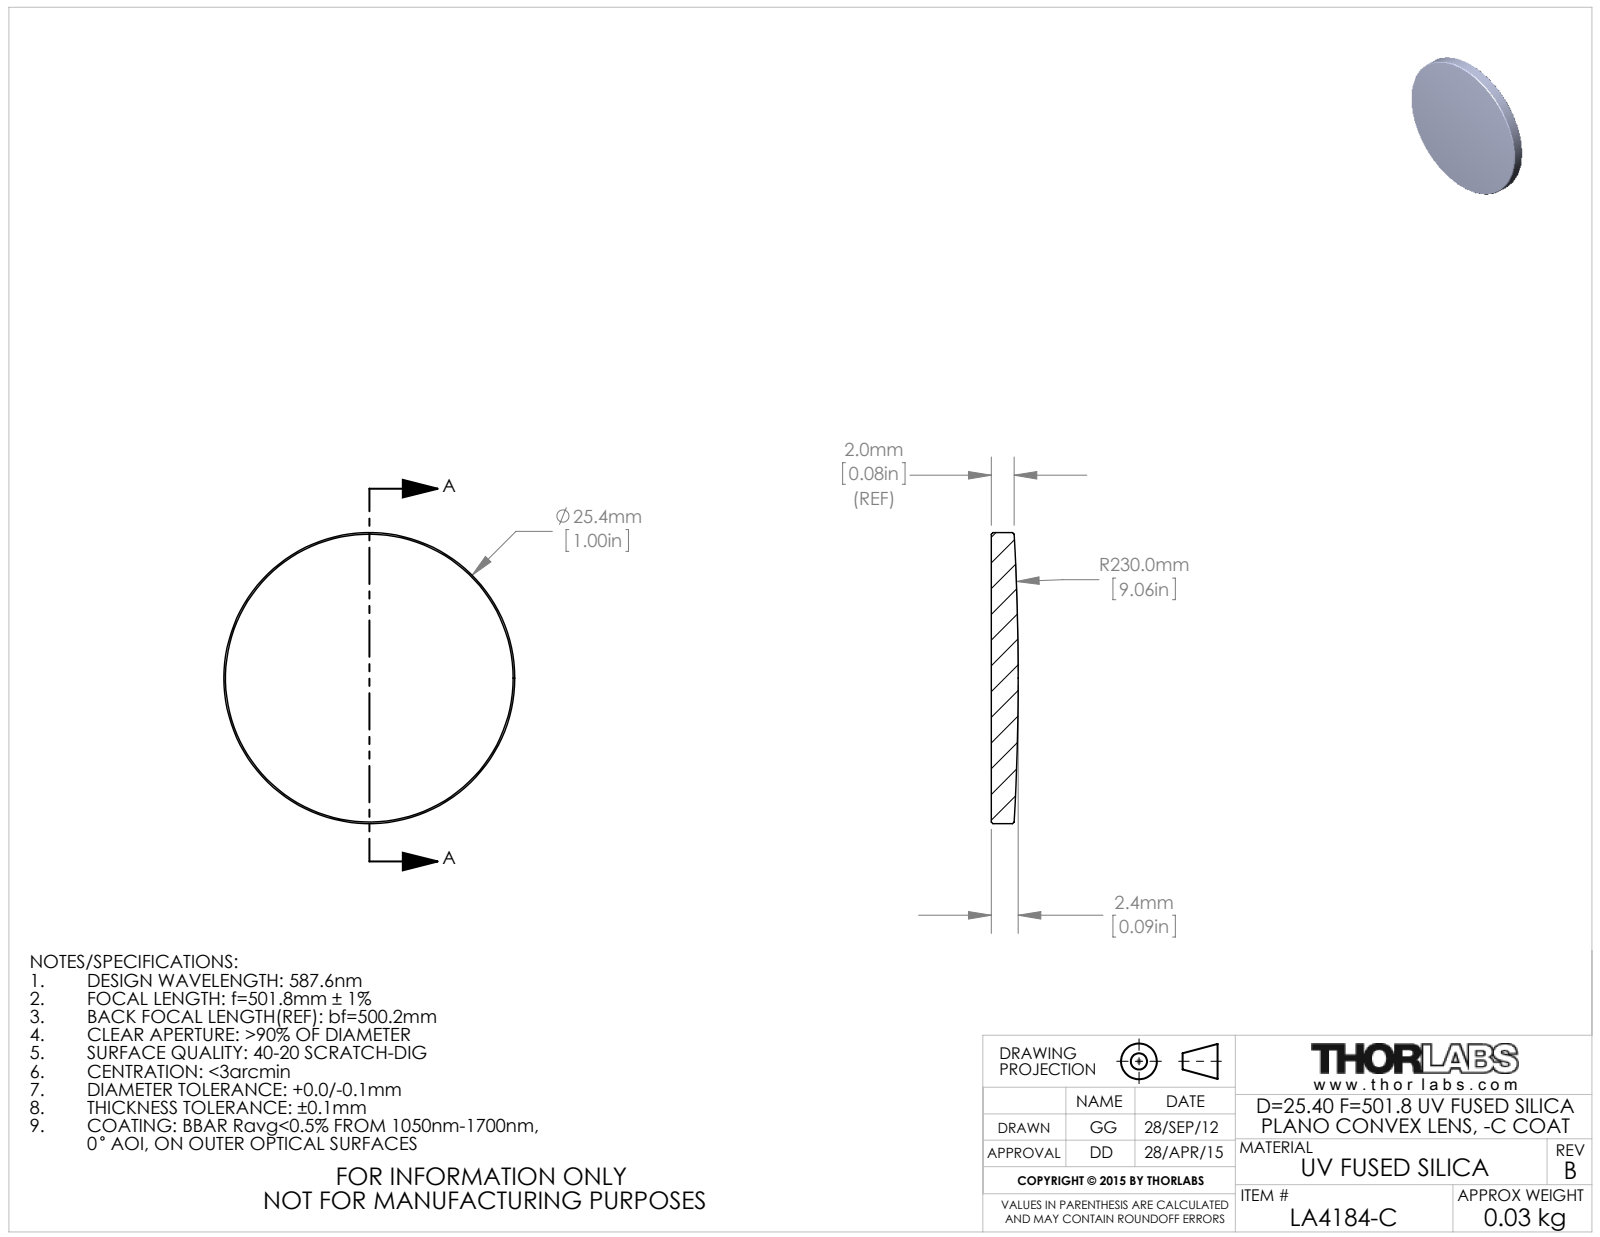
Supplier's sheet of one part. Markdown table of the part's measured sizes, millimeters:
| quantity | value |
| --- | --- |
| part name | 25004-E0W |
| STEP written by | SolidWorks 2014 (CONFIG_CONTROL_DESIGN) |
| units | millimeters |
| bodies | 1 solid, 9 faces (1 planar, 2 cylindrical, 6 other) |
| overall size | 25.4 × 25.4 × 2.35 |
| volume | 1 101 mm³ |
| surface area | 1 161 mm² |
| round bosses / shafts (diameter × count) | 25.4 × 1 |
